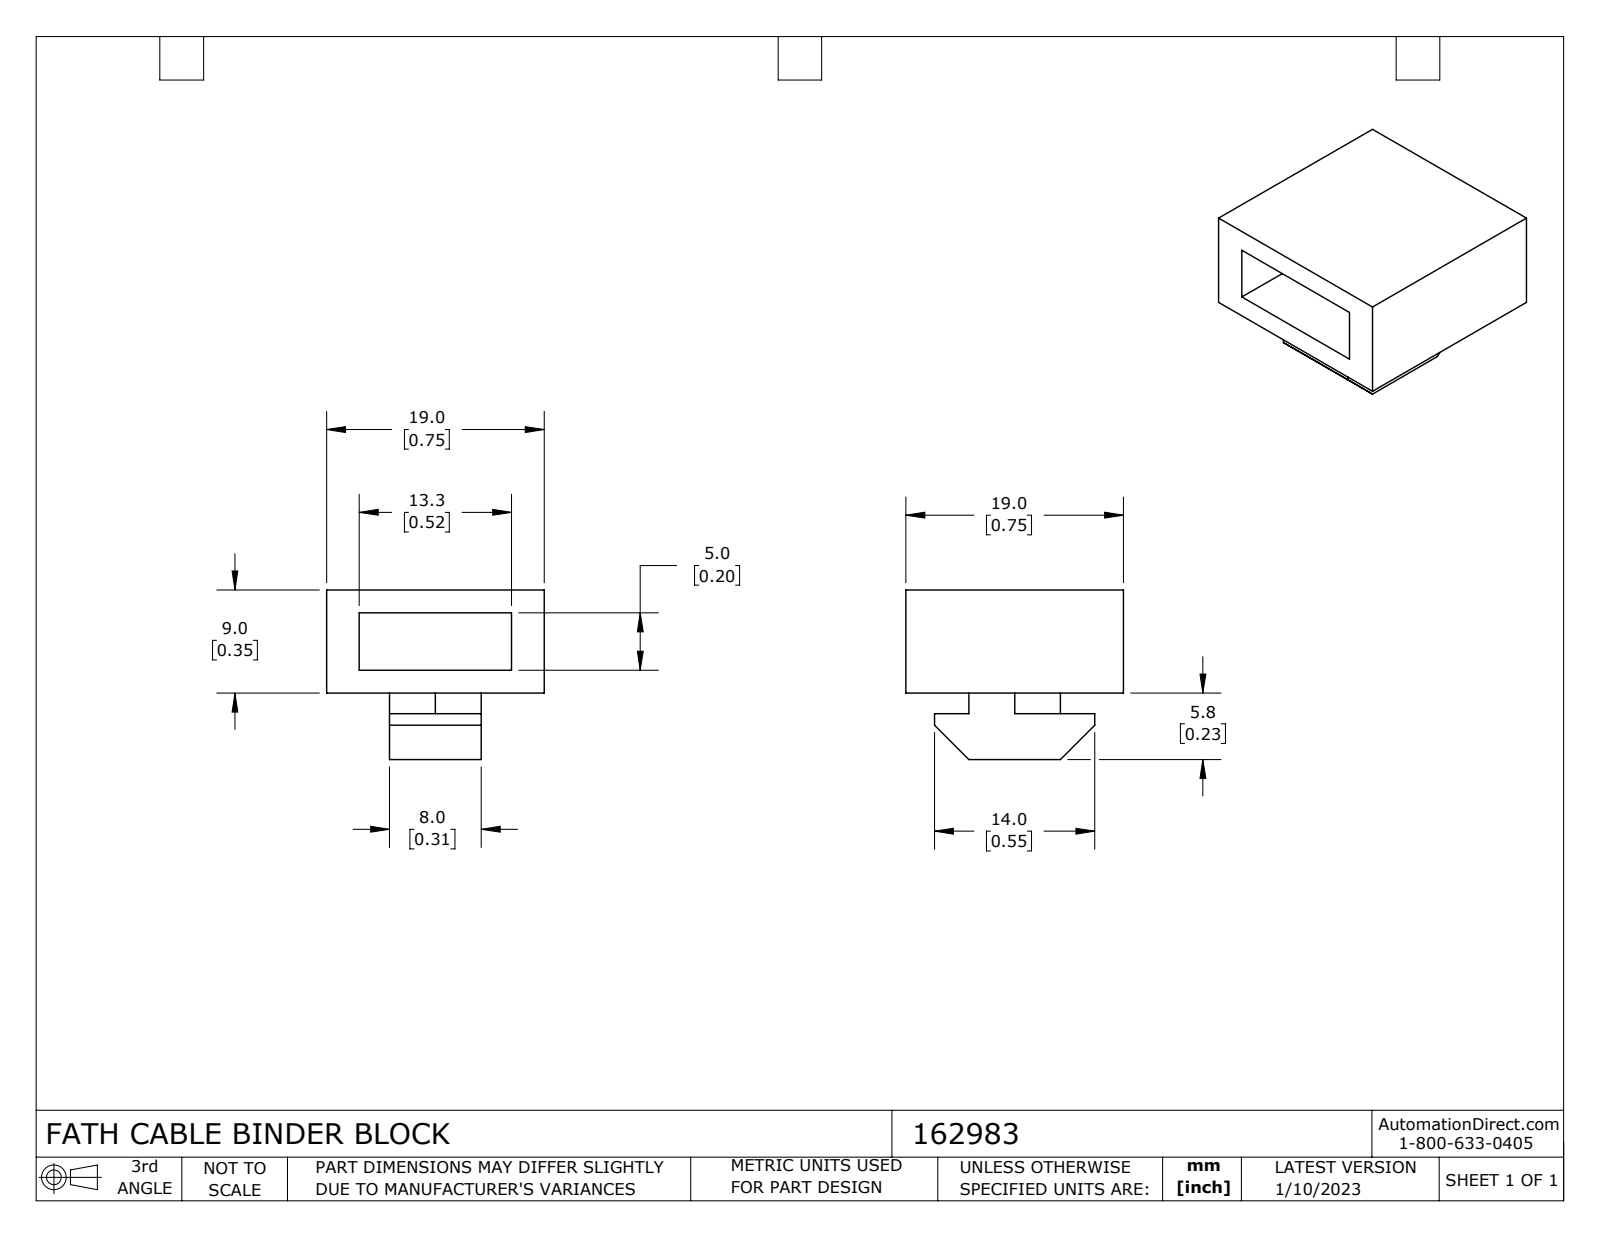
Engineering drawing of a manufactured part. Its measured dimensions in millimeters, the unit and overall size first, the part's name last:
Units: millimetres
Overall size (bounding box): 19 × 19 × 14.8
Partial cylindrical surfaces — rounded edges, fillets, slot ends (radius × count): R4 ×1
Main face-to-face distances: 2, 7, 9, 19, 5, 2.8, 16.2, 5.5, 13.5, 2.6
Volume: 2 460 mm³ · Surface area: 2 259 mm²
Bodies: 1 solid, 23 faces (21 planar, 2 cylindrical, 0 other)
Part name (STEP PRODUCT): 162983
STEP written by: SolidWorks 2021 (CONFIG_CONTROL_DESIGN)
